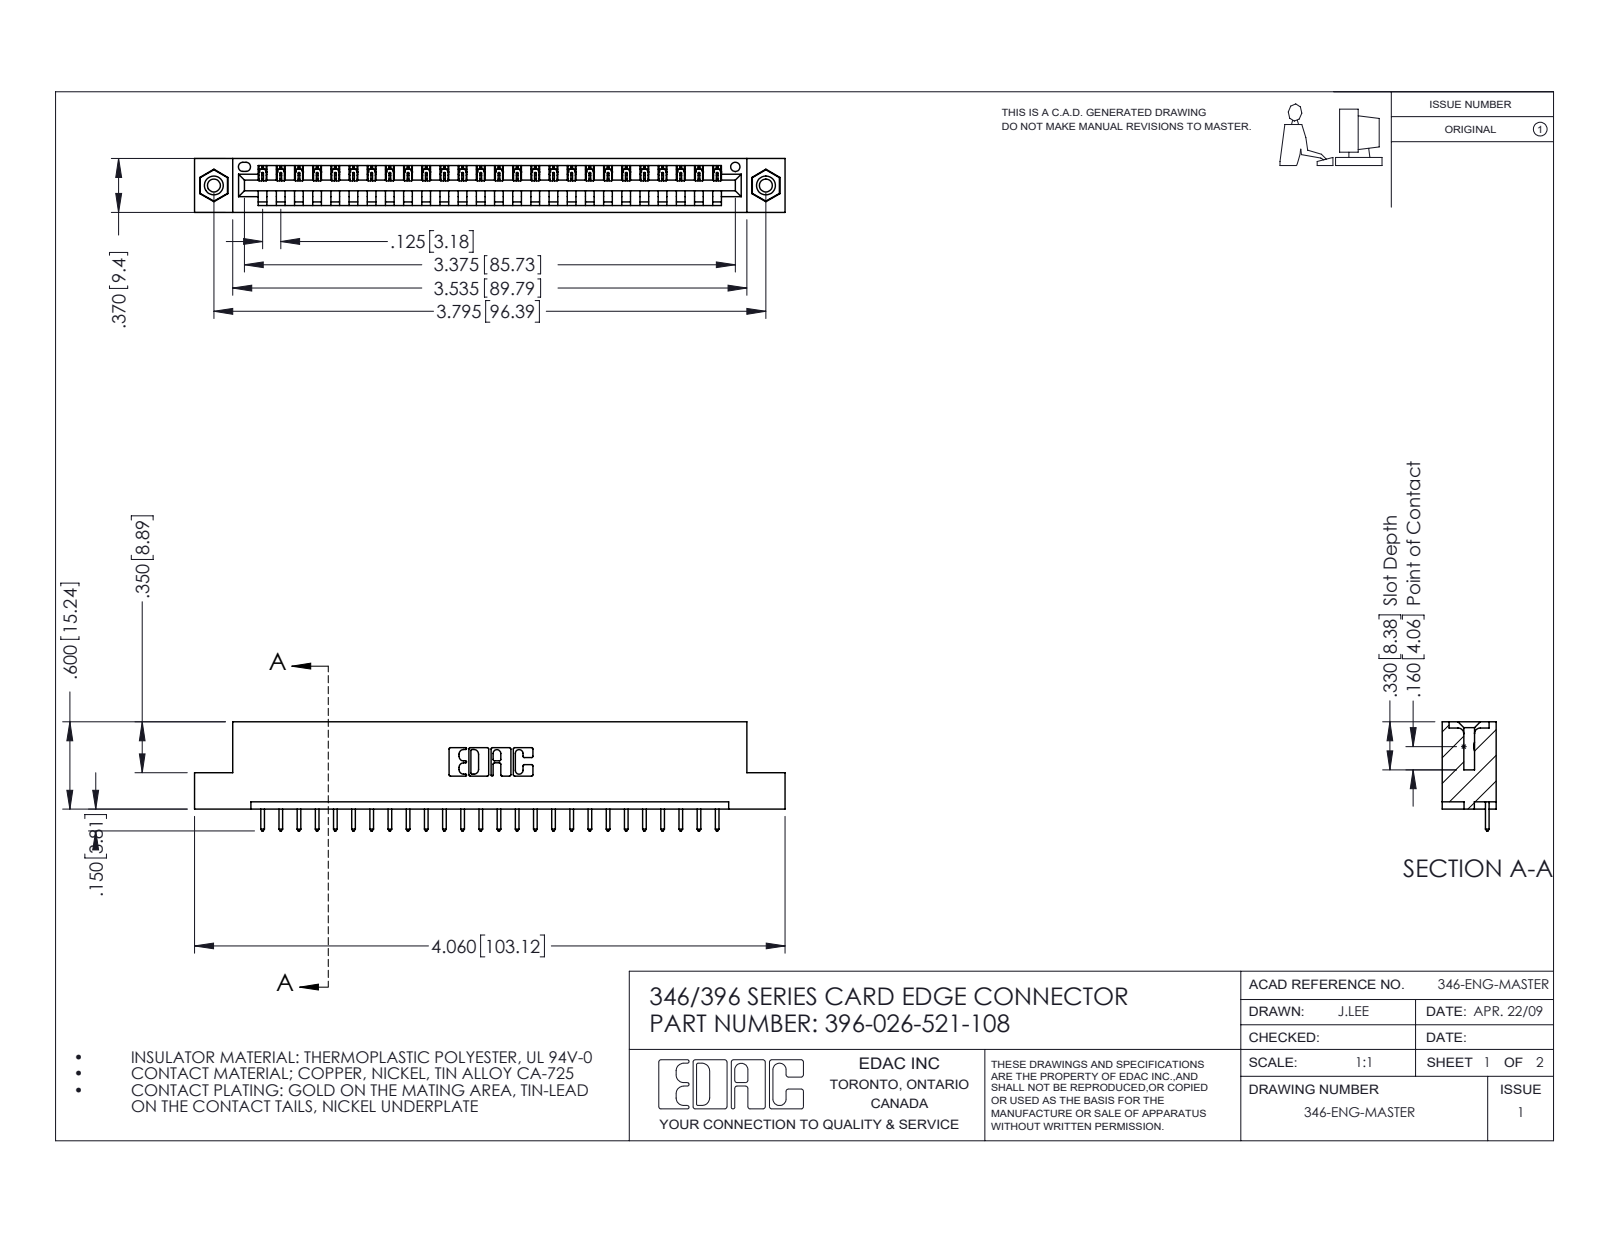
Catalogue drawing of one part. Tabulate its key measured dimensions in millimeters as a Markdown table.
| quantity | value |
| --- | --- |
| part name | 396-026-521-108; 345-250-001_345-250-003-102; 345-292-001_345-293-121; 346 Part_Flush Mounting Lugs - 0.156 Dia-TI |
| STEP written by | SolidWorks 2016 (CONFIG_CONTROL_DESIGN) |
| units | millimeters |
| bodies | 29 solids, 1690 faces (1148 planar, 526 cylindrical, 16 other) |
| overall size | 103.1 × 19.1 × 9.4 |
| volume | 9 680 mm³ |
| surface area | 11 650 mm² |
| round holes (diameter × count) | 2.3 × 2, 3.2 × 2, 4 × 2, 1.6 × 1 |
| round bosses / shafts (diameter × count) | 3.9 × 2 |
| partial cylindrical surfaces (radius × count) | 0.2 × 52, 0.3 × 52, 0.3 × 22, 0.2 × 6, 0.8 × 6, 0.7 × 3, 0.8 × 2, 1 × 2 |
| main face-to-face distances | 1.2, 8.2, 9.4, 6.4, 1.8, 7.6, 0.6, 3.8, 5.6, 2.5 |
| hole center spacings | 6.2, 91.1, 96.4 |
